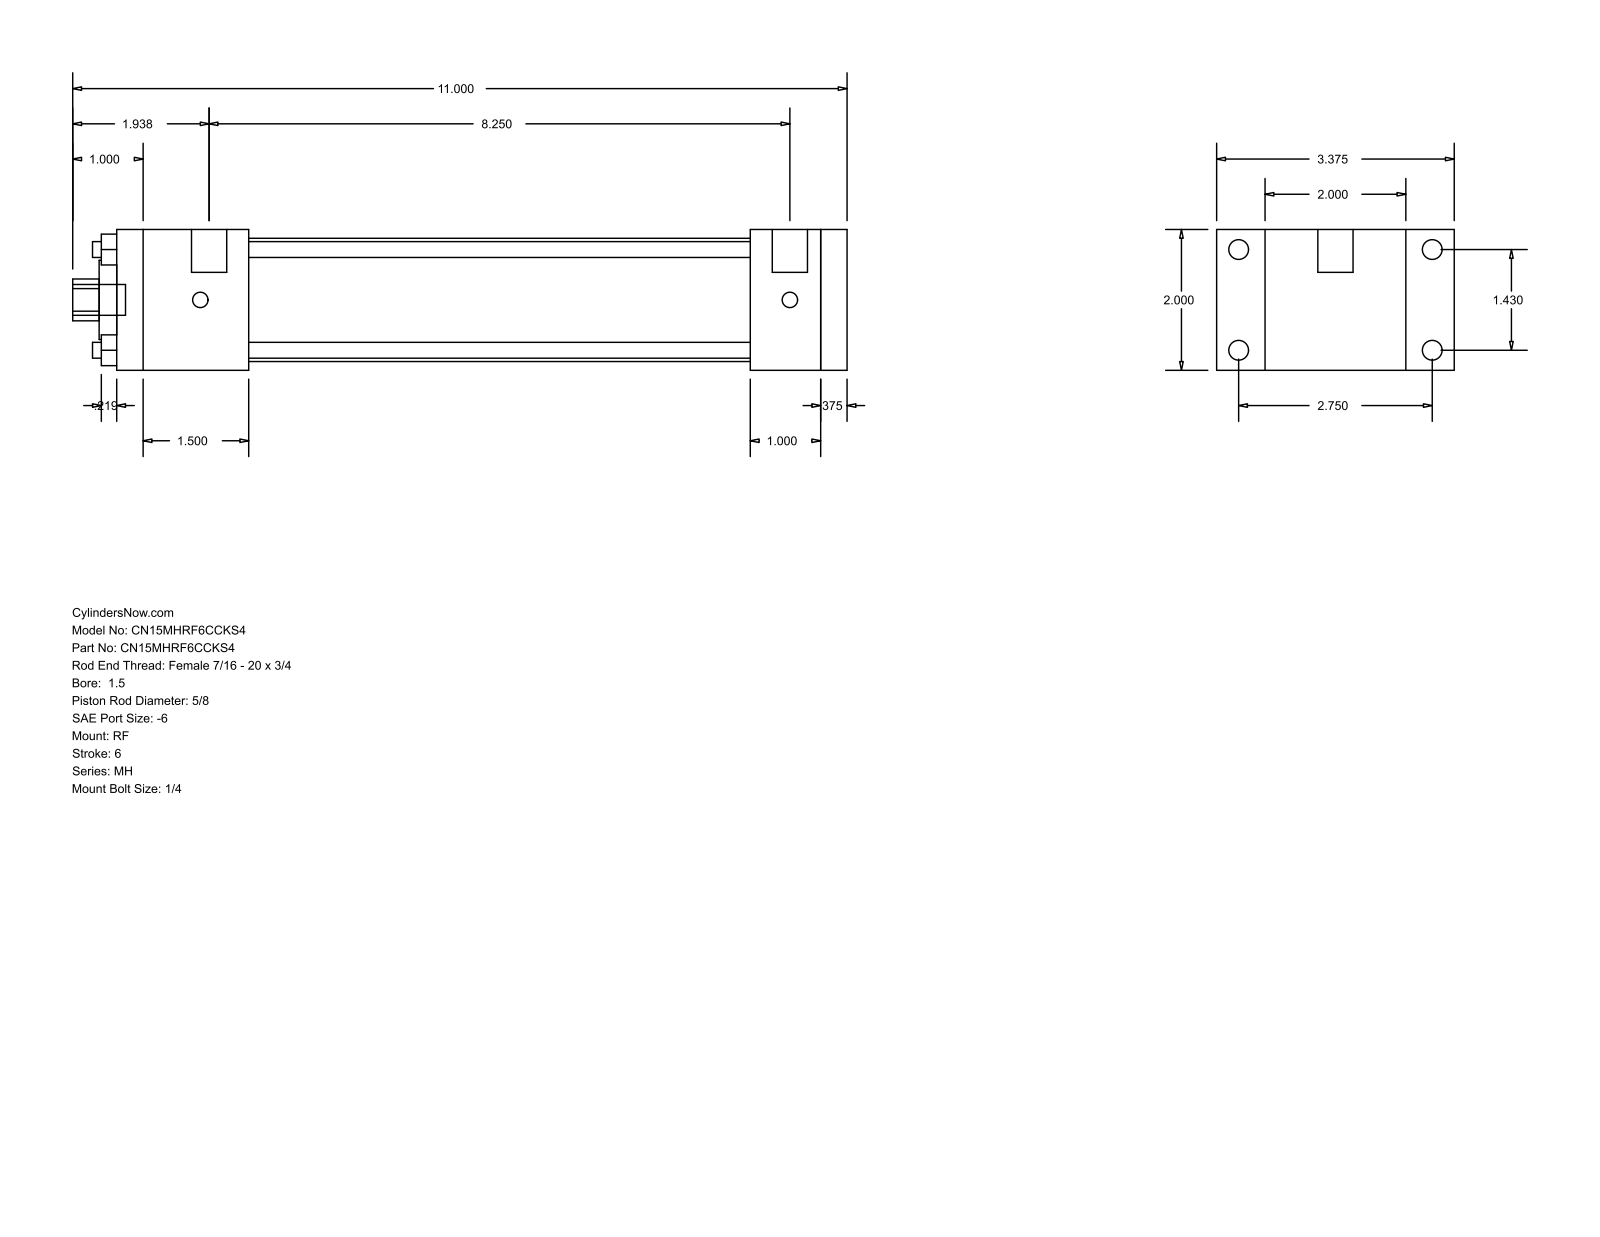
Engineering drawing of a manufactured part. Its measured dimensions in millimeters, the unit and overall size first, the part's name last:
Units: millimetres
Overall size (bounding box): 279.4 × 85.72 × 50.8
Round holes (diameter × count): ⌀5.71 ×4, ⌀15.88 ×1, ⌀28.57 ×1, ⌀44.45 ×1
Round bosses / shafts (diameter × count): ⌀7.14 ×4, ⌀5.56 ×4, ⌀12.7 ×2, ⌀11.11 ×1
Partial cylindrical surfaces — rounded edges, fillets, slot ends (radius × count): R7.54 ×1
Main face-to-face distances: 50.8, 9.52, 254, 263.52, 17.46, 68.26, 228.59, 25.41, 34.93, 47.62
Hole centre spacings: 25.68, 36.32, 51.36
Bodies: 0 solids, 92 faces (64 planar, 28 cylindrical, 0 other)
Part name (STEP PRODUCT): MH_RF__0150_0.625
STEP written by: GSSL Pune (CONFIG_CONTROL_DESIGN)
